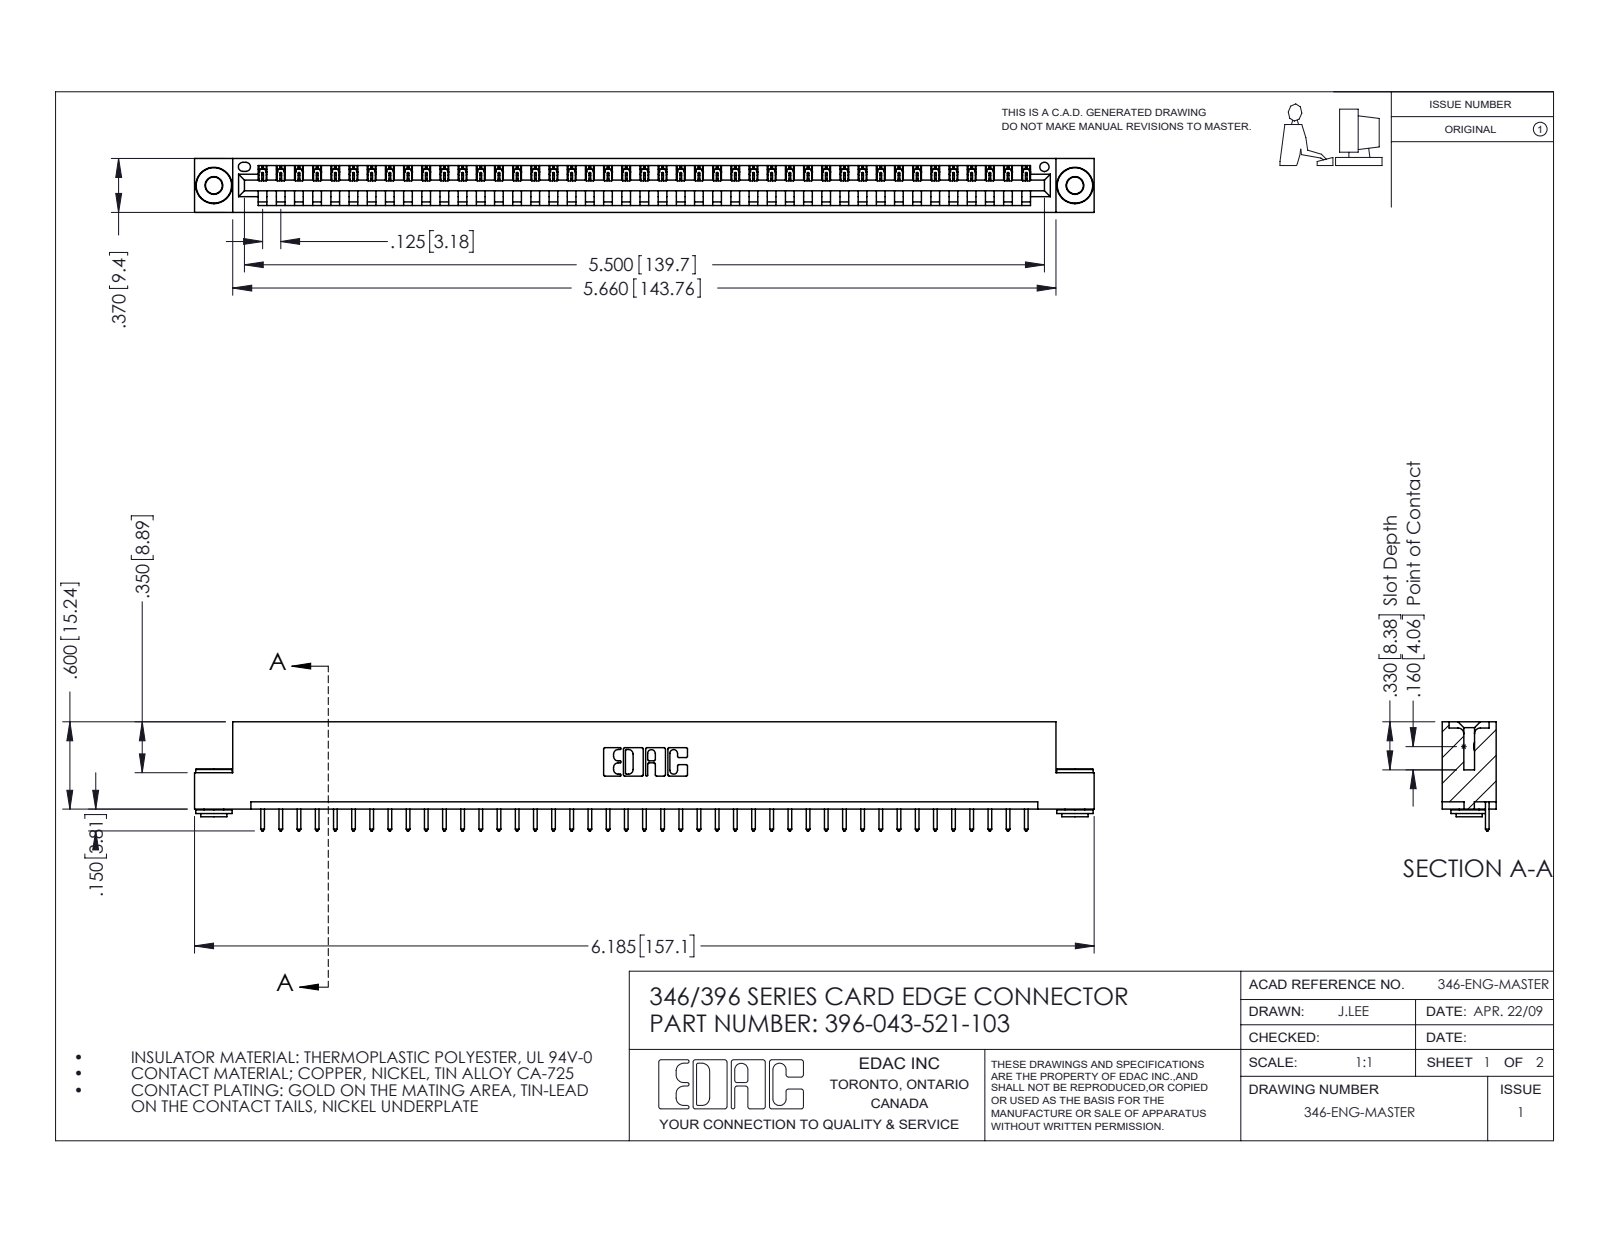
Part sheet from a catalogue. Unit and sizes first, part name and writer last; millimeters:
Units: millimetres
Overall size (bounding box): 157.1 × 19.1 × 9.4
Round holes (diameter × count): ⌀2.9 ×2, ⌀4 ×2, ⌀1.6 ×1
Round bosses / shafts (diameter × count): ⌀6.4 ×2, ⌀4.6 ×2, ⌀3.5 ×2
Partial cylindrical surfaces — rounded edges, fillets, slot ends (radius × count): R0.2 ×86, R0.3 ×86, R0.3 ×22, R0.2 ×6, R0.8 ×6, R0.7 ×3, R0.8 ×2, R1 ×2
Main face-to-face distances: 1.2, 8.2, 9.4, 6.4, 0.6, 1.8, 7.6, 3.8, 5.6, 2.5
Hole centre spacings: 6.2, 145.1, 150.4
Volume: 14 900 mm³ · Surface area: 18 420 mm²
Bodies: 46 solids, 2654 faces (1806 planar, 840 cylindrical, 8 other)
Part name (STEP PRODUCT): 345-250-002_345-250-002-102; 396-043-521-103; 345-292-001_345-293-121; 346 Part_Flush Mounting Lugs - 0.156 Dia-TH
STEP written by: SolidWorks 2016 (CONFIG_CONTROL_DESIGN)
